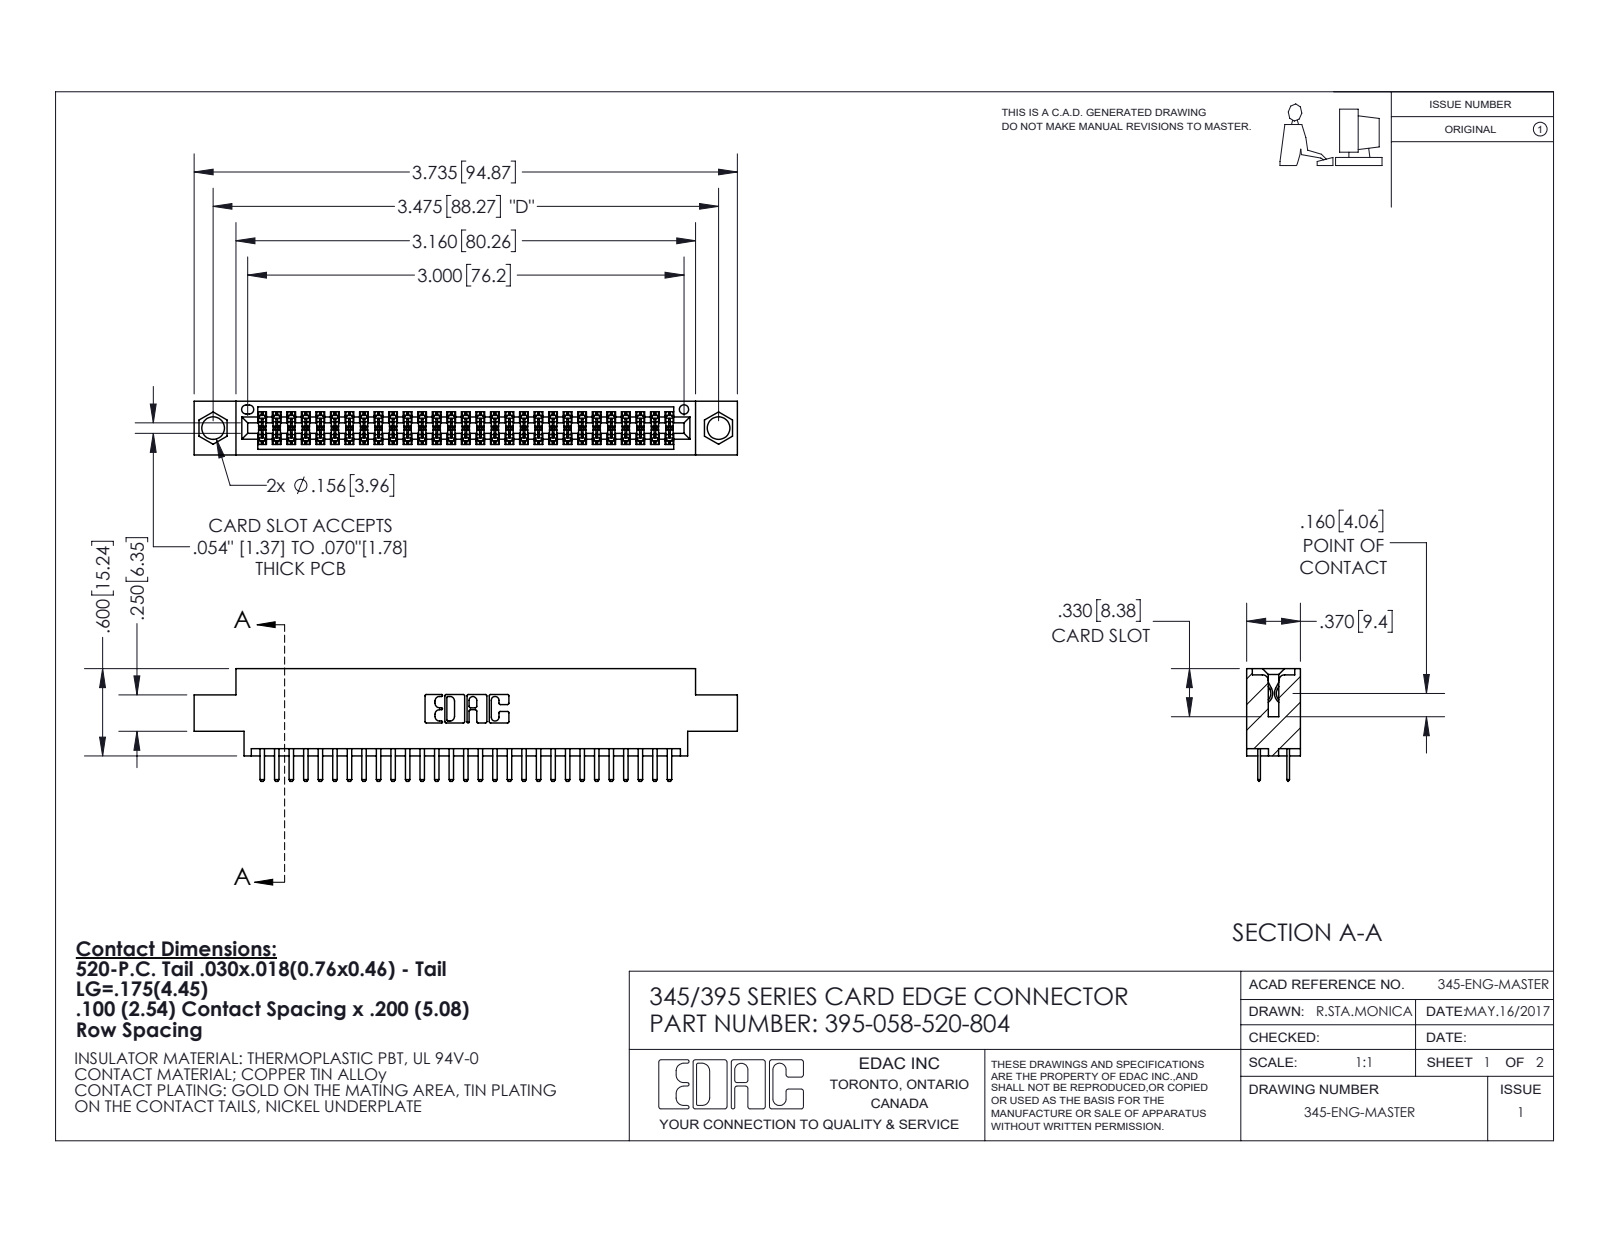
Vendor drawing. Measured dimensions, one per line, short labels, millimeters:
name: 345 Part_0.170 Offset - 0.156 Dia-TI; 395-058-520-804; 345-292-001_345-293-120
written by: SolidWorks 2020 (CONFIG_CONTROL_DESIGN)
unit: mm
bodies: 59 solids, 3276 faces (2128 planar, 1148 cylindrical, 0 other)
size: 94.9 × 19.7 × 9.4
volume: 8 850 mm³; area: 12 770 mm²
holes: 2× ⌀4, 1× ⌀1.6
rounds: 116× R0.2, 62× R0.3, 22× R0.3, 6× R0.2, 6× R0.8, 3× R0.7, 2× R0.4, 2× R0.5
face distances: 1.8, 7.6, 5.1, 9.4, 2.5, 6.9, 0.6, 5.7, 0.6, 4.4
hole spacings: 6.9, 82.3, 88.3
